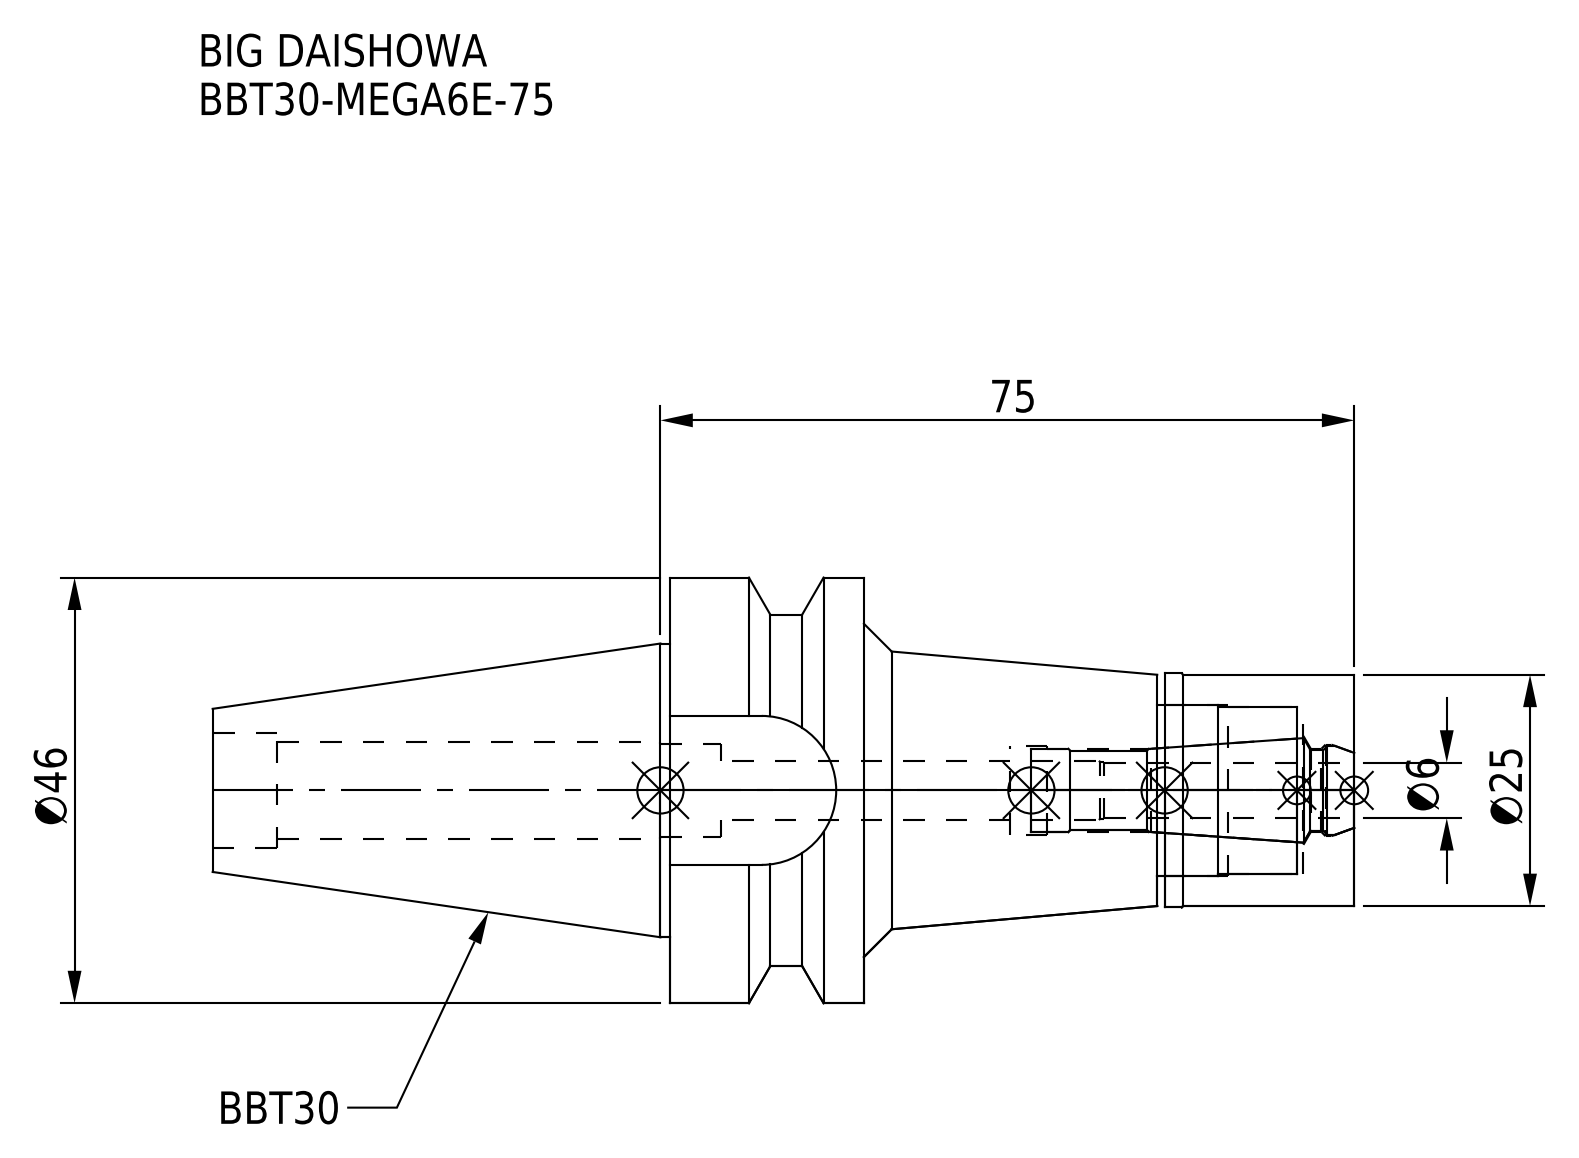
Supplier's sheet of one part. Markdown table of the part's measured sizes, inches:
| quantity | value |
| --- | --- |
| part name | BBT30ME06075-060_ASM.stp; MEN6_1.stp; BBT30-MEGA6E-75-060.stp; BBT30-MEGA6E-75-060-FreeParts (+3 more) |
| STEP written by | SolidWorks 2019 (CONFIG_CONTROL_DESIGN) |
| units | inches |
| bodies | 2 solids, 79 faces (21 planar, 38 cylindrical, 20 other) |
| overall size | 4.858 × 1.811 × 1.811 |
| volume | 4.581 in³ |
| surface area | 31.5 in² |
| round holes (diameter × count) | 0.252 × 1, 0.354 × 1, 0.378 × 1, 0.39 × 1, 0.394 × 1, 0.409 × 1, 0.492 × 1, 0.709 × 1, 0.728 × 1 |
| round bosses / shafts (diameter × count) | 1.811 × 1, 1.25 × 1, 0.996 × 1, 0.984 × 1 |
| partial cylindrical surfaces (radius × count) | 0.317 × 1, 0.748 × 1 |
| main face-to-face distances | 0.827, 2.087, 2.913, 1.248, 1.283, 0.807, 1.28, 2.106, 0.839, 0.031 |
